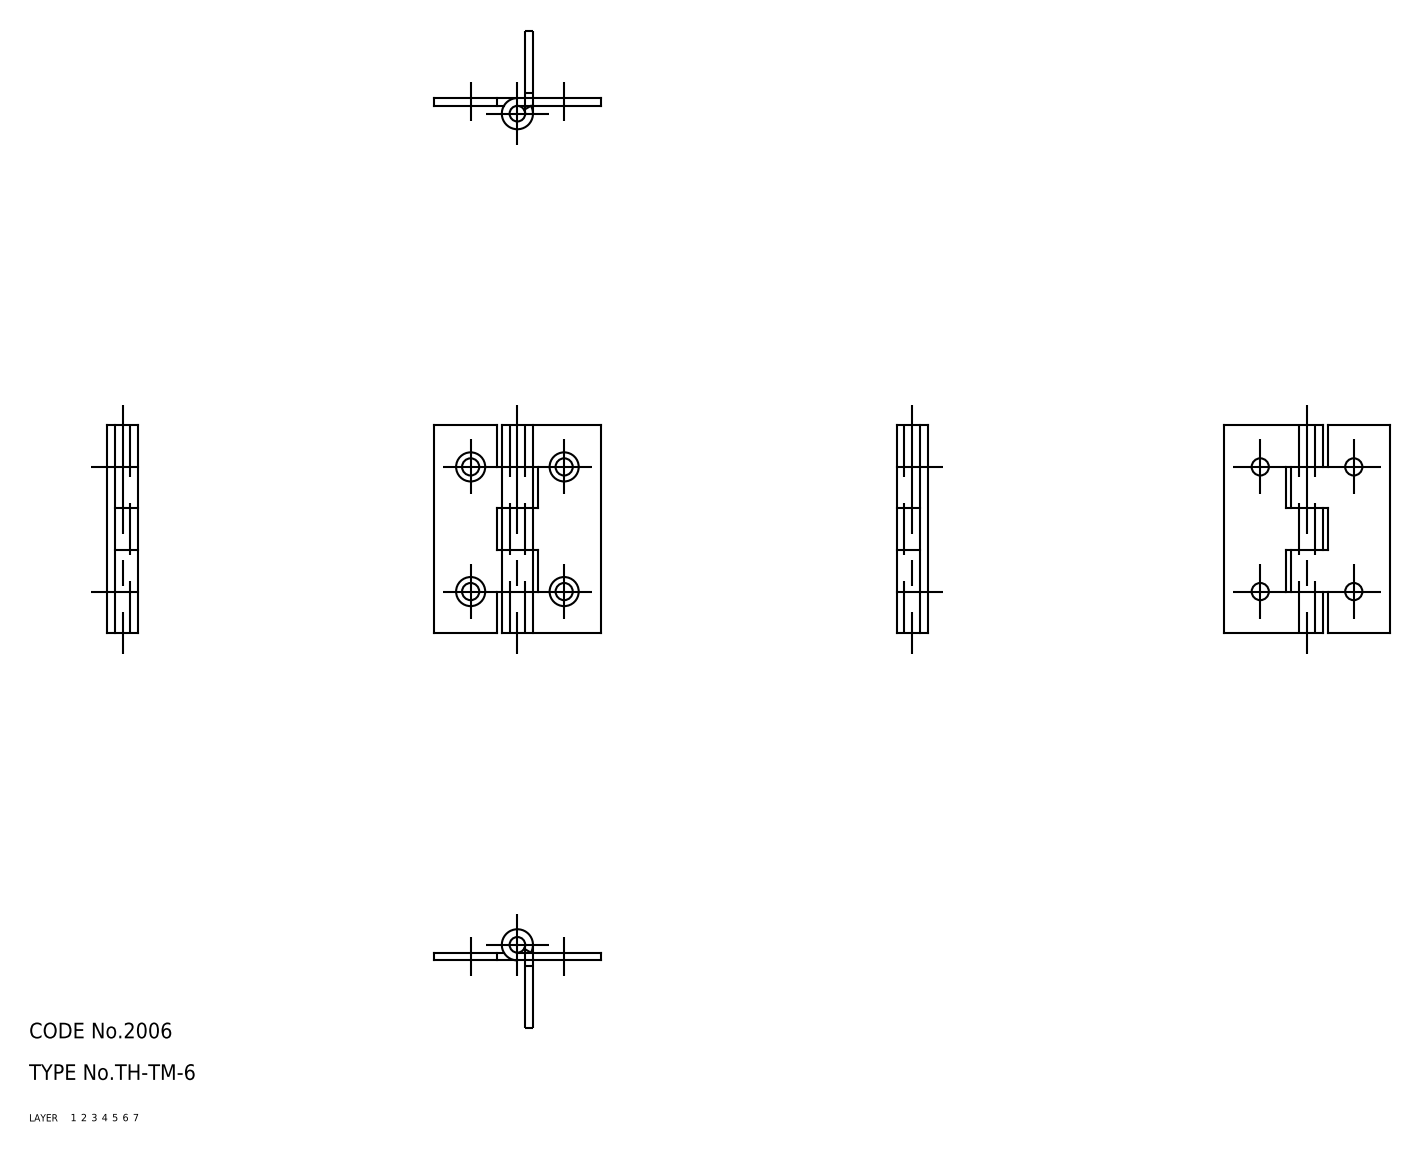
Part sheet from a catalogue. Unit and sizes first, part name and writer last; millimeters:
Units: millimetres
Overall size (bounding box): 40 × 32 × 6
Volume: 2 582 mm³ · Surface area: 4 091 mm²
Bodies: 3 solids, 58 faces (0 planar, 0 cylindrical, 58 other)
Part name (STEP PRODUCT): shaft; hinge piece_B; hinge piece_A; TH_TM_6_24420_36
STEP written by: CADfix (AUTOMOTIVE_DESIGN)
